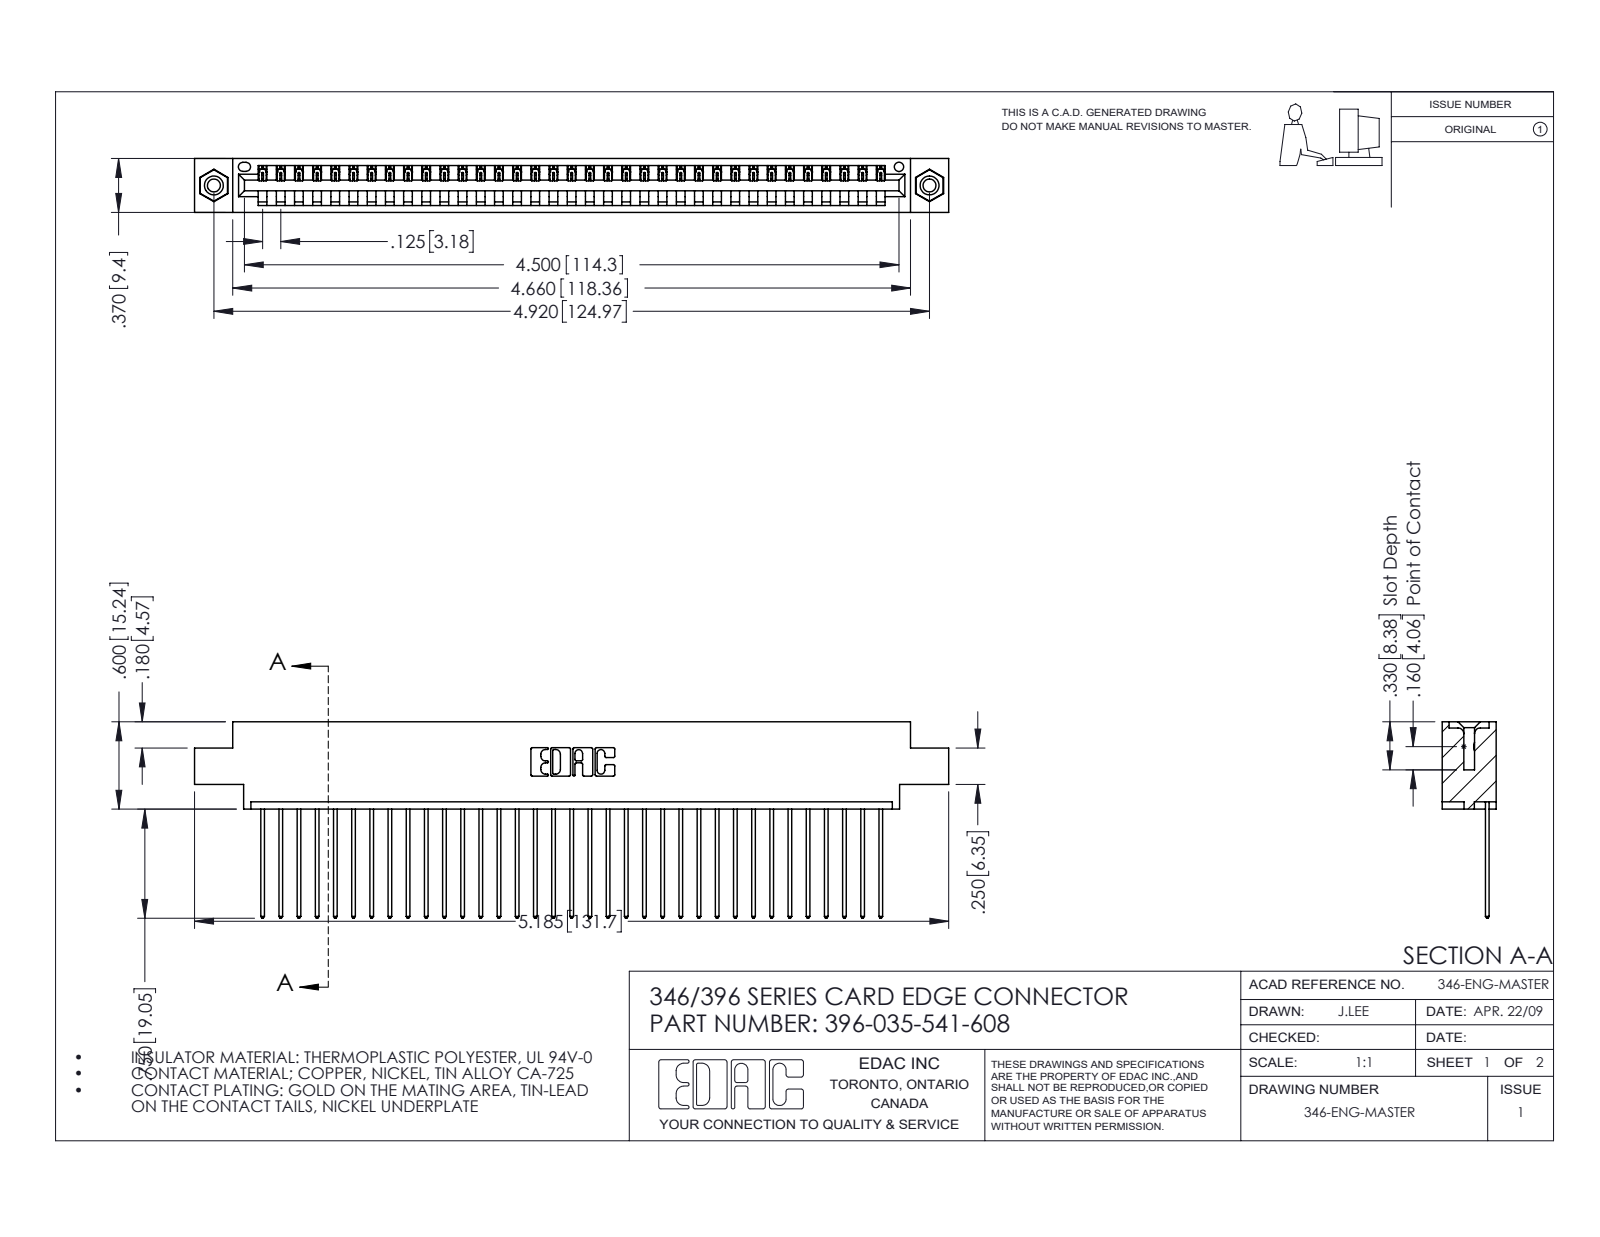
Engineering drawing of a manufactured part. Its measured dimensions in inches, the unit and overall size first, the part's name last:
Units: inches
Overall size (bounding box): 5.185 × 1.35 × 0.37
Round holes (diameter × count): ⌀0.089 ×2, ⌀0.125 ×2, ⌀0.156 ×2, ⌀0.064 ×1
Round bosses / shafts (diameter × count): ⌀0.155 ×2
Partial cylindrical surfaces — rounded edges, fillets, slot ends (radius × count): R0.006 ×70, R0.01 ×70, R0.01 ×22, R0.007 ×6, R0.031 ×6, R0.026 ×3, R0.031 ×2, R0.04 ×2
Main face-to-face distances: 0.048, 0.322, 0.37, 0.25, 0.072, 0.298, 0.025, 0.222, 0.148, 0.1
Hole centre spacings: 0.246, 4.711, 4.92
Volume: 0.764 in³ · Surface area: 25.48 in²
Bodies: 38 solids, 2216 faces (1512 planar, 688 cylindrical, 16 other)
Part name (STEP PRODUCT): 346 Part_0.170 Offset - 0.156 Dia-TI; 345-292-001_345-293-141; 396-035-541-608; 345-250-001_345-250-003-102
STEP written by: SolidWorks 2016 (CONFIG_CONTROL_DESIGN)
